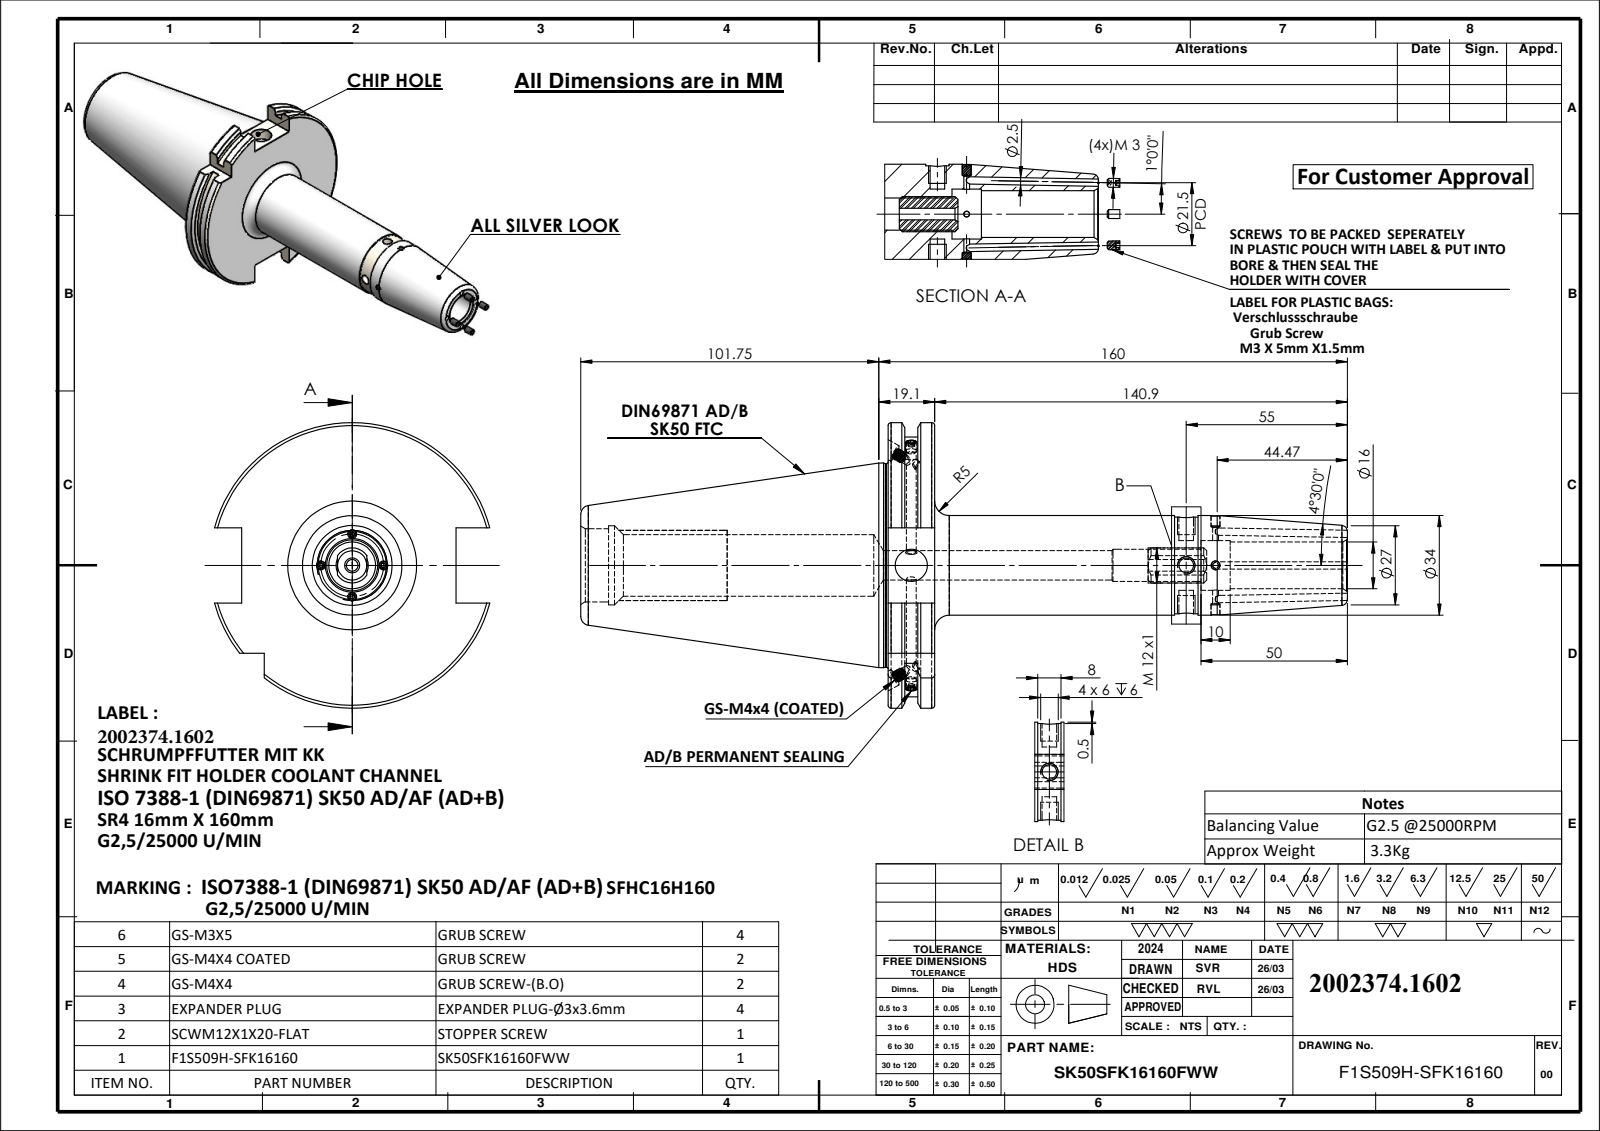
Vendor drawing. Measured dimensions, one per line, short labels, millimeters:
name: F1S509H-SFK16160; EXPANDER PLUG Ø3x3.6; GS-M4X4_DIN 913 - M4 x 4-N; GS-M3X5 (+3 more)
written by: SolidWorks 2024 (CONFIG_CONTROL_DESIGN)
unit: mm
bodies: 14 solids, 443 faces (137 planar, 134 cylindrical, 172 other)
size: 269.77 × 97.5 × 94.05
volume: 425 877 mm³; area: 68 202 mm²
holes: 4× ⌀2.5, 2× ⌀2, 2× ⌀3, 2× ⌀3.2, 2× ⌀5, 2× ⌀6, 2× ⌀11, 1× ⌀3.3, 1× ⌀4, 1× ⌀10, 1× ⌀16, 1× ⌀17
bosses: 4× ⌀4, 4× ⌀3, 2× ⌀2.9, 1× ⌀69.85, 1× ⌀69.45, 1× ⌀34, 1× ⌀33
rounds: 1× R6, 1× R44.9, 1× R48.75
face distances: 15.9, 5.66, 10.24, 10.14, 4.48, 5.76, 104.95, 110.61, 115.09, 120.85
hole spacings: 10, 93.9, 103.9
